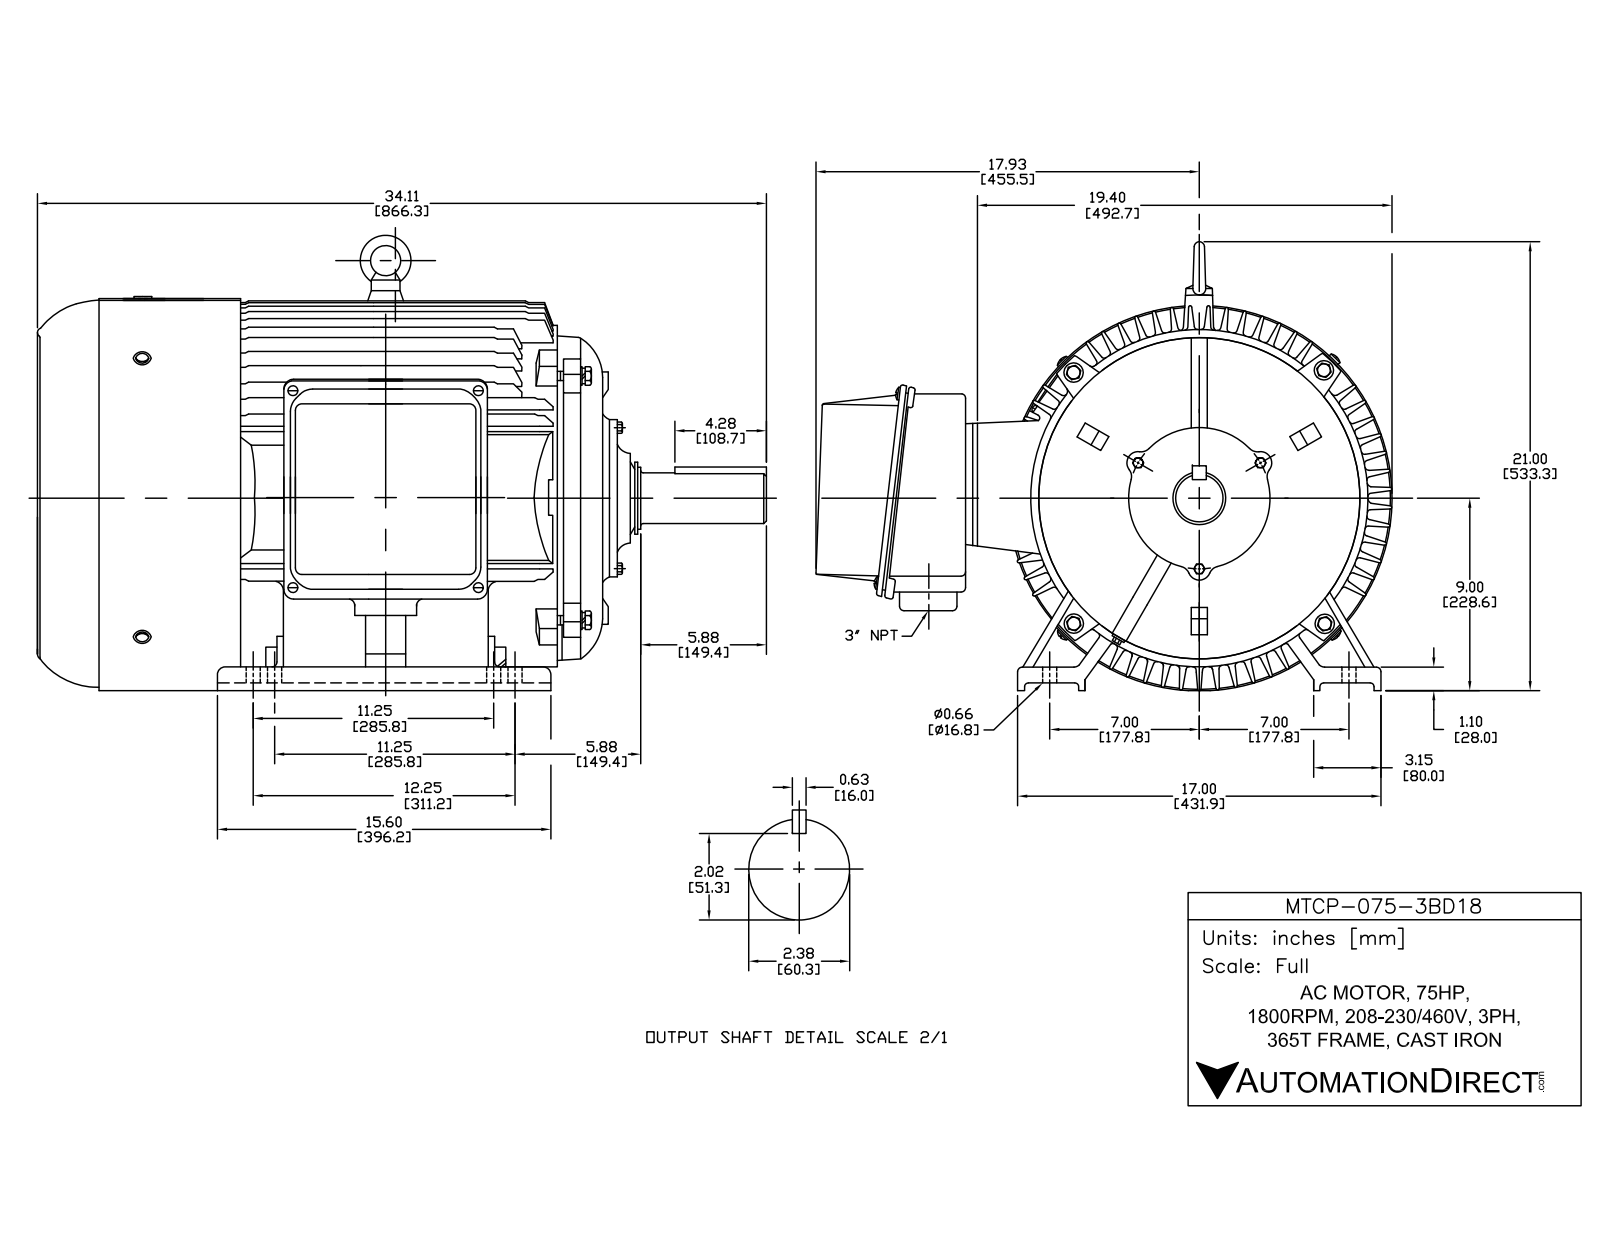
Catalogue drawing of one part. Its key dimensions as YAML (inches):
part_name: "plain washers-n series-grade a gb_GB_FASTENER_WASHER_PWNA 6; PE360接线盒座_默认_按加工; PE360前轴承外盖加工件; MTCP365T (+8 more)"
step_written_by: "SolidWorks 2017 (AUTOMOTIVE_DESIGN)"
units: inches
bodies: {solids: 64, faces: 4227, planar: 1096, cylindrical: 1579, other: 1552}
overall_size: [34.311, 26.456, 21.37]
volume: 1250
surface_area: 7652
round_holes:
  - {diameter: 0.394, count: 19}
  - {diameter: 0.268, count: 10}
  - {diameter: 0.669, count: 8}
  - {diameter: 0.472, count: 5}
  - {diameter: 0.197, count: 4}
  - {diameter: 0.236, count: 4}
  - {diameter: 0.252, count: 4}
  - {diameter: 0.263, count: 4}
  - {diameter: 0.402, count: 4}
  - {diameter: 0.508, count: 4}
  - {diameter: 0.512, count: 4}
  - {diameter: 0.591, count: 4}
round_bosses_or_shafts:
  - {diameter: 0.472, count: 8}
  - {diameter: 0.315, count: 8}
  - {diameter: 0.945, count: 4}
  - {diameter: 0.752, count: 4}
  - {diameter: 0.394, count: 4}
  - {diameter: 0.389, count: 4}
  - {diameter: 0.236, count: 4}
  - {diameter: 18.937, count: 1}
partial_cylinders:
  - {radius: 0.039, count: 235}
  - {radius: 0.197, count: 152}
  - {radius: 0.02, count: 83}
  - {radius: 0.079, count: 65}
  - {radius: 0.059, count: 39}
  - {radius: 0.236, count: 34}
  - {radius: 0.472, count: 20}
  - {radius: 0.177, count: 18}
face_to_face_distances: [0.236, 0.059, 0.315, 0.551, 0.197, 26.713, 26.654, 1.123, 18.976, 8.898]
hole_center_spacings: [5.118, 2.953, 3.248, 5.372, 3.111, 8.976, 0.295, 1]
